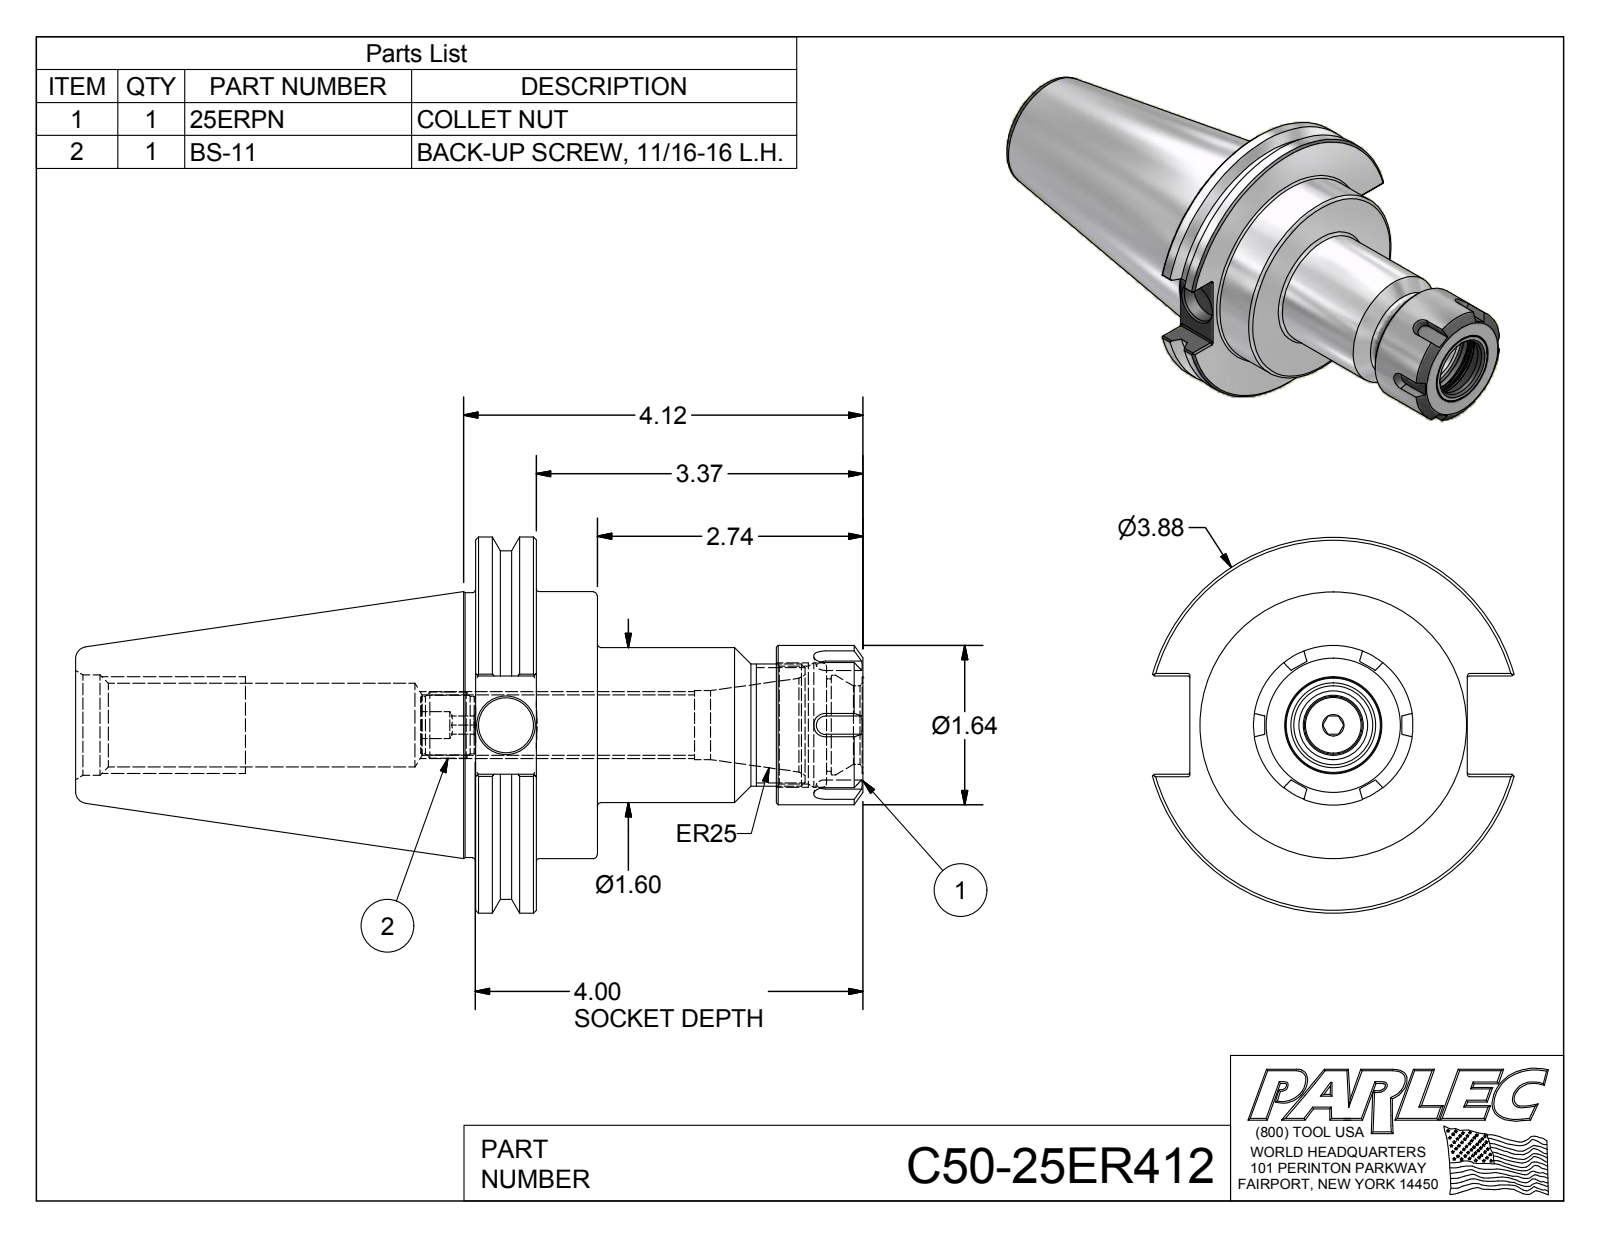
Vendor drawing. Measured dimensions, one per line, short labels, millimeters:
name: C50-25ER412; C50-25ER4-1; 25ERPN; BS-11
written by: Autodesk Inventor 2012 (AUTOMOTIVE_DESIGN)
unit: mm
bodies: 3 solids, 146 faces (59 planar, 37 cylindrical, 50 other)
size: 206.2 × 98.4 × 94.7
volume: 446 400 mm³; area: 64 840 mm²
holes: 1× ⌀7.1, 1× ⌀14.3, 1× ⌀15.7, 1× ⌀18, 1× ⌀20.6, 1× ⌀22, 1× ⌀24.1, 1× ⌀26.1, 1× ⌀26.4, 1× ⌀30.9, 1× ⌀32.5
bosses: 1× ⌀98.4, 1× ⌀91.3, 1× ⌀69.9, 1× ⌀69.3, 1× ⌀41.7, 1× ⌀40.5, 1× ⌀32, 1× ⌀17.3
rounds: 12× R0.5
face distances: 15.9, 16, 31.9, 101.5, 85.6, 69.6, 78.8, 62.9, 46.9, 22.7
